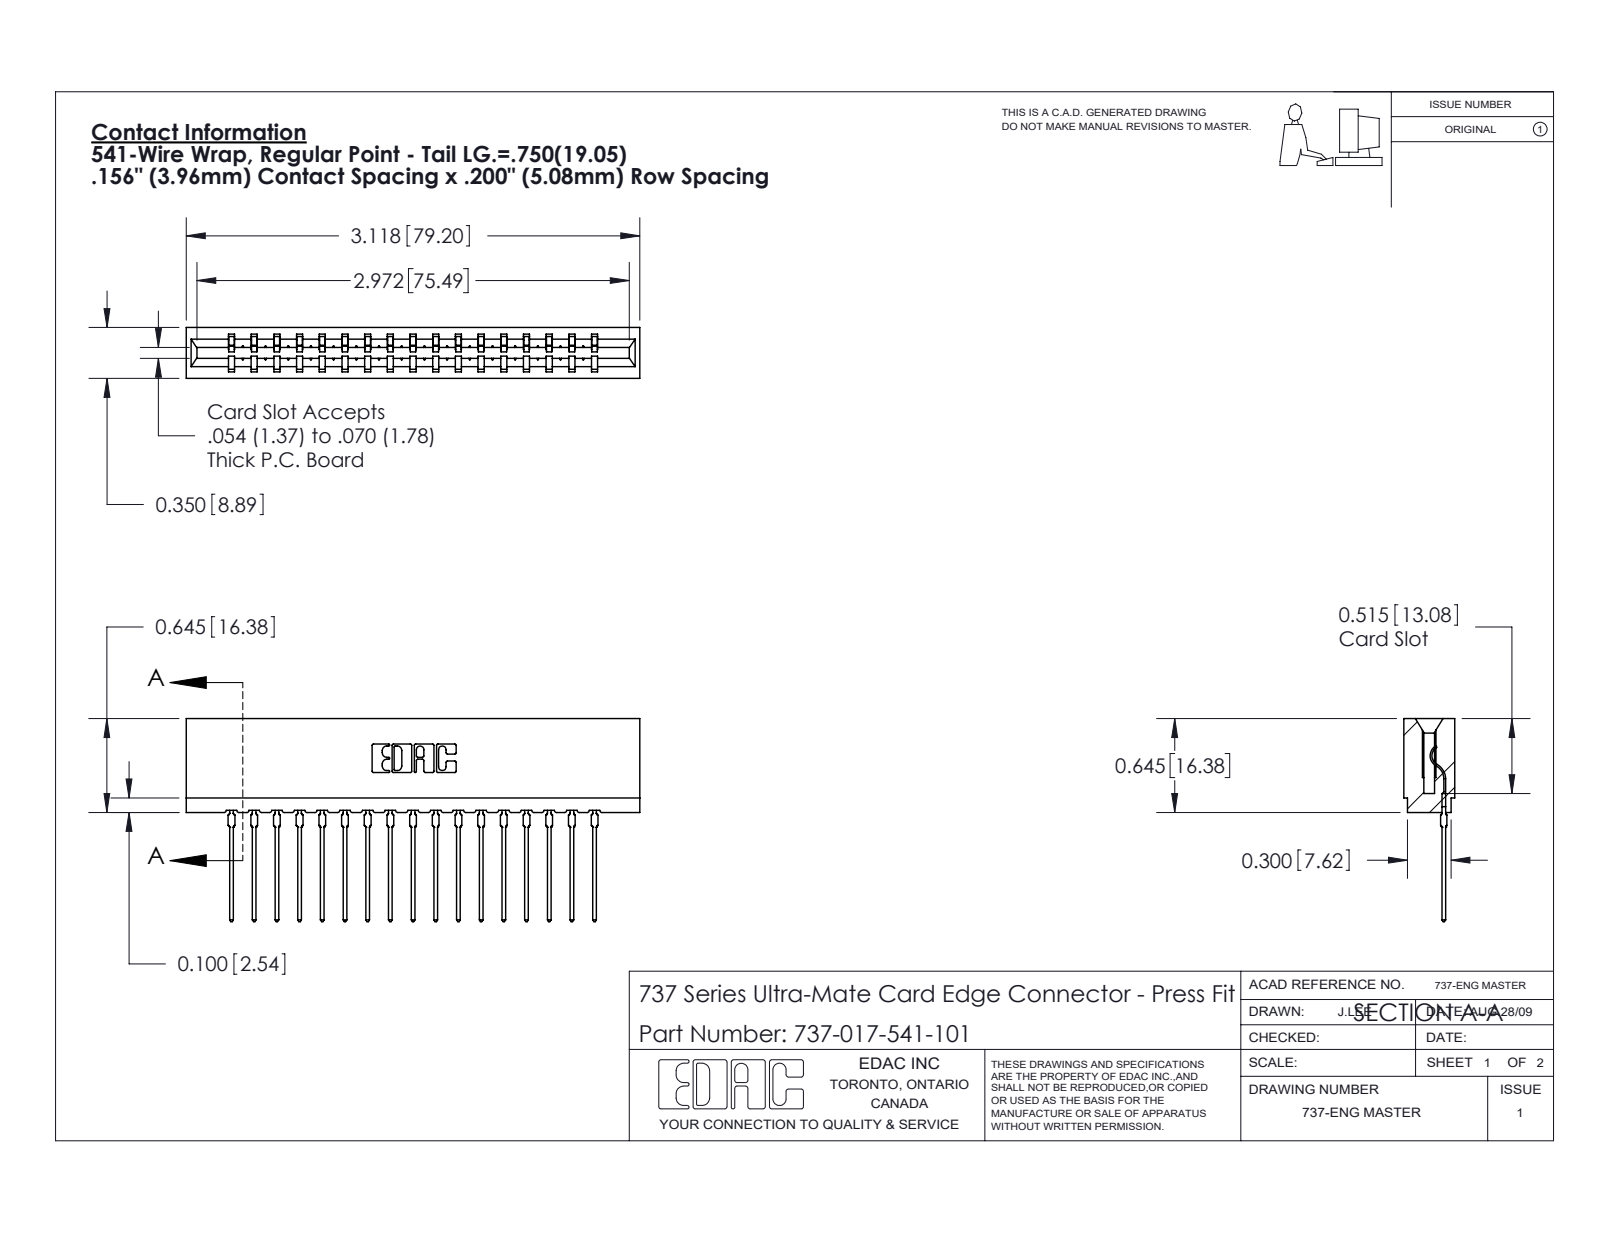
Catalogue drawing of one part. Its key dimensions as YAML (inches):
part_name: "737 Part_Insulator Option - 01; 745-292-001_541; 737-017-541-101"
step_written_by: "SolidWorks 2020 (CONFIG_CONTROL_DESIGN)"
units: inches
bodies: {solids: 18, faces: 2015, planar: 1210, cylindrical: 363, other: 442}
overall_size: [3.118, 1.396, 0.35]
volume: 0.482
surface_area: 16.31
partial_cylinders:
  - {radius: 0.015, count: 34}
  - {radius: 0.021, count: 34}
  - {radius: 0.01, count: 22}
  - {radius: 0.007, count: 6}
  - {radius: 0.031, count: 6}
  - {radius: 0.005, count: 4}
  - {radius: 0.011, count: 4}
  - {radius: 0.026, count: 3}
face_to_face_distances: [0.138, 0.212, 0.35, 0.156, 0.624, 0.78, 0.074, 0.468, 0.063, 0.287]
